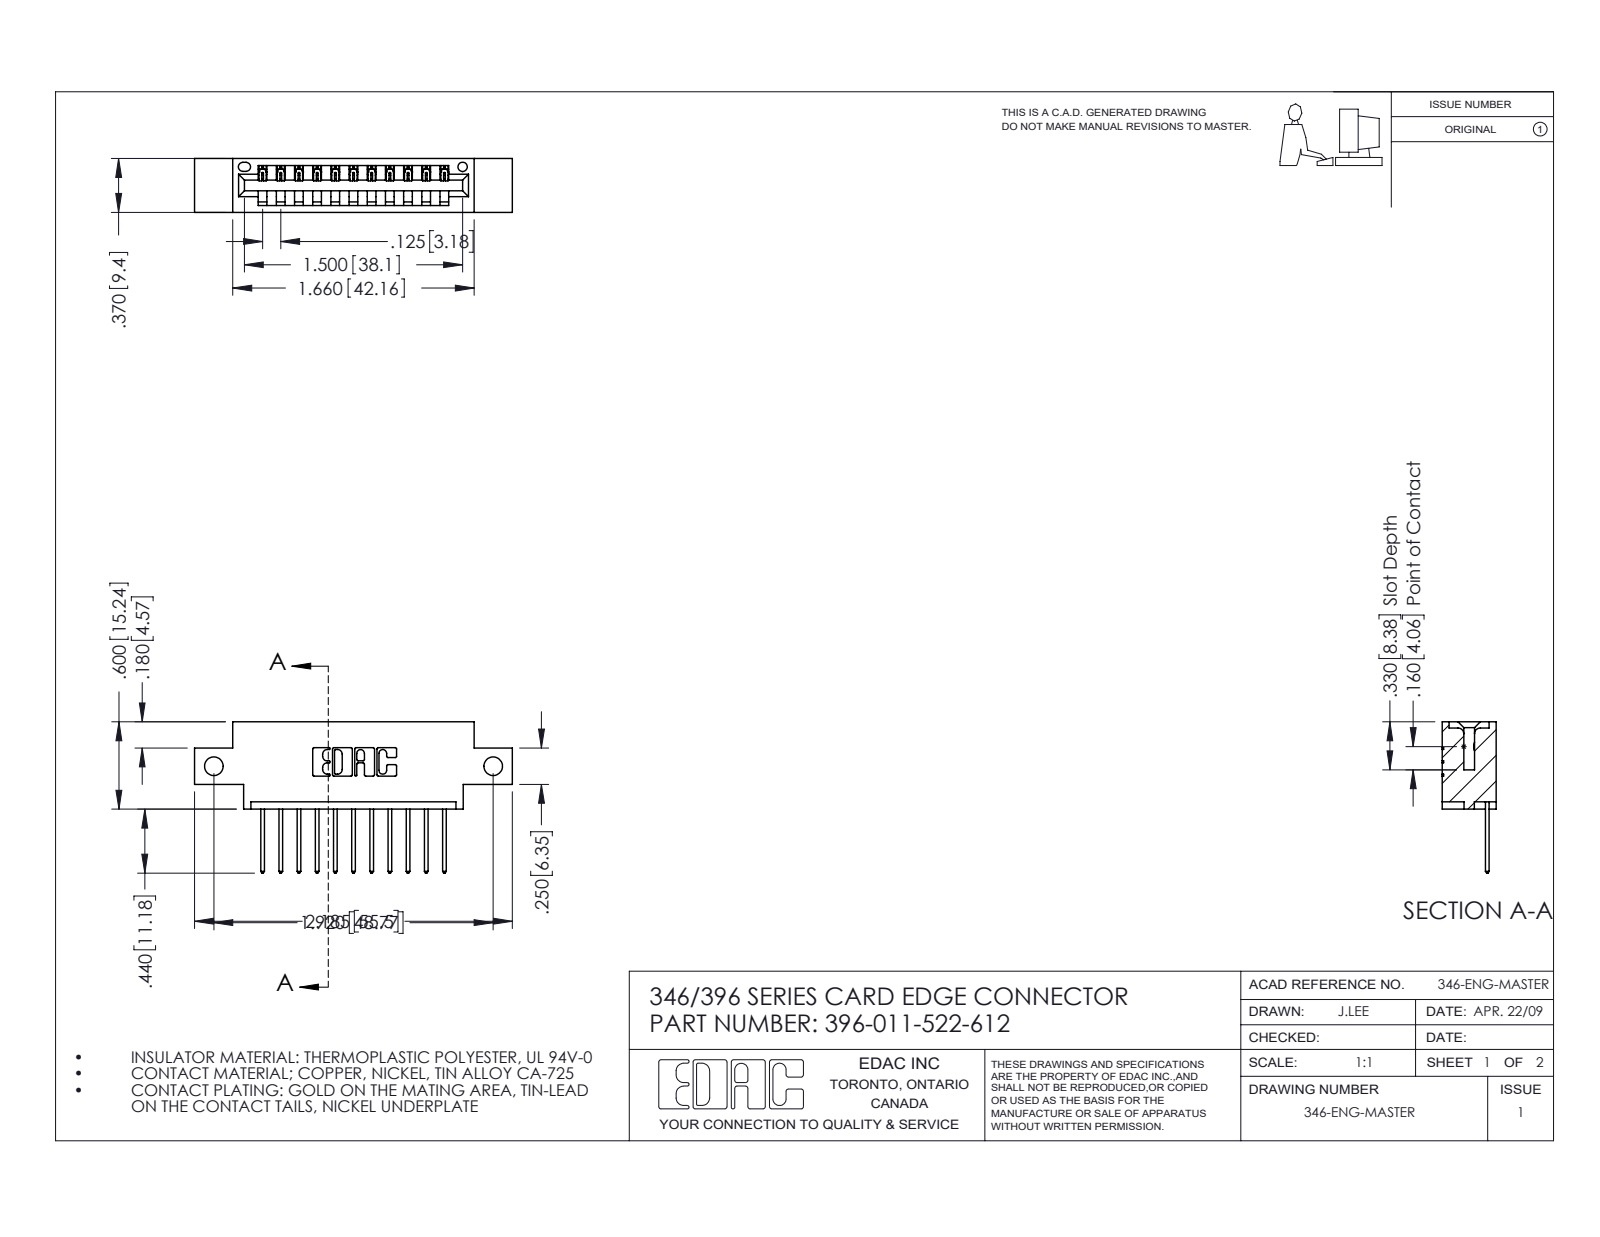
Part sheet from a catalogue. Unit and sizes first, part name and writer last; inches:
Units: inches
Overall size (bounding box): 2.185 × 1.04 × 0.37
Round holes (diameter × count): ⌀0.128 ×2, ⌀0.064 ×1
Partial cylindrical surfaces — rounded edges, fillets, slot ends (radius × count): R0.006 ×22, R0.01 ×22, R0.01 ×22, R0.007 ×6, R0.031 ×6, R0.026 ×3, R0.031 ×2, R0.04 ×2
Main face-to-face distances: 0.25, 0.37, 0.048, 0.322, 0.072, 0.298, 0.025, 0.148, 0.222, 0.1
Hole centre spacings: 1.92
Volume: 0.296 in³ · Surface area: 8.979 in²
Bodies: 12 solids, 764 faces (520 planar, 244 cylindrical, 0 other)
Part name (STEP PRODUCT): 345-292-001_345-293-122; 346 Part_0.170 Offset - Side Mount; 396-011-522-612
STEP written by: SolidWorks 2016 (CONFIG_CONTROL_DESIGN)
